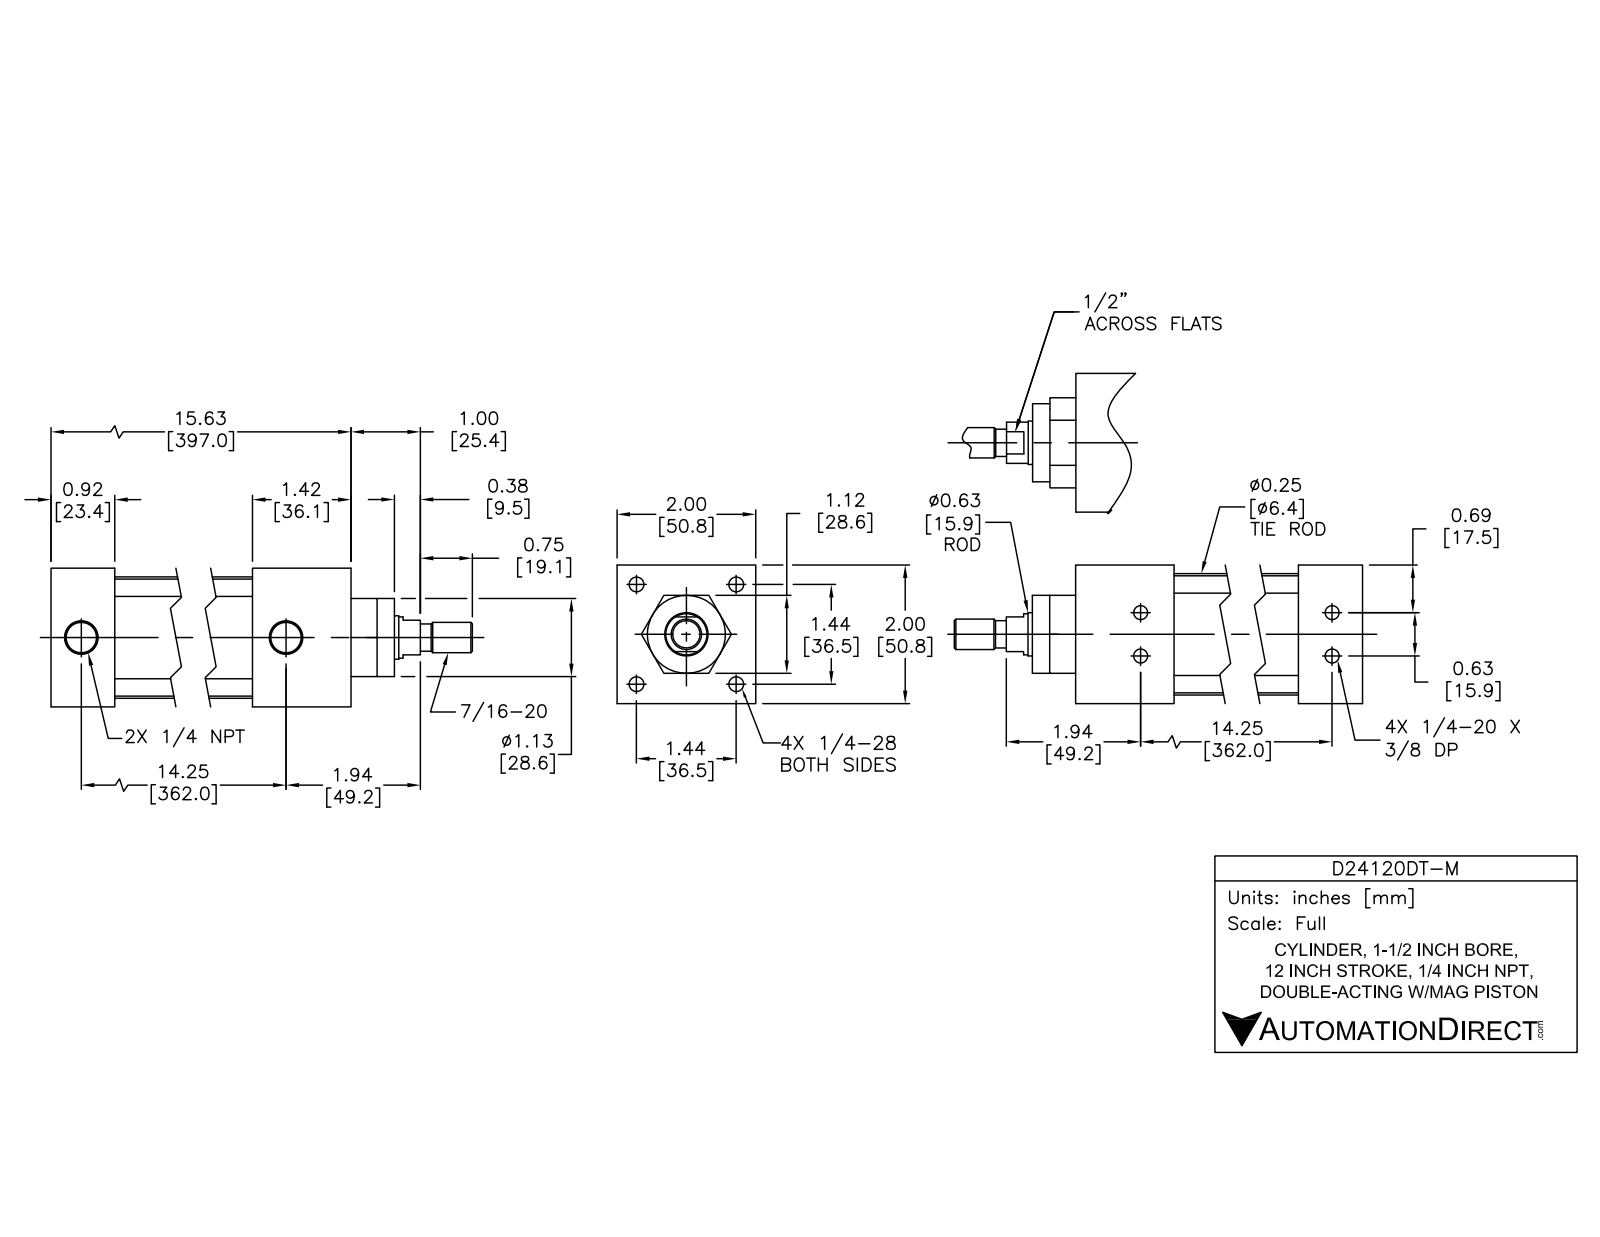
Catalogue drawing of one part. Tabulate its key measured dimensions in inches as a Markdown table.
| quantity | value |
| --- | --- |
| part name | D24120DT-M BODY; D24120DT-M PISTON; D24120DT-M |
| STEP written by | SolidWorks 2015 (AUTOMOTIVE_DESIGN) |
| units | inches |
| bodies | 12 solids, 303 faces (99 planar, 114 cylindrical, 90 other) |
| overall size | 17.371 × 2 × 2 |
| volume | 25.85 in³ |
| surface area | 272.5 in² |
| round holes (diameter × count) | 0.196 × 4, 0.211 × 4, 0.281 × 4, 0.406 × 4, 0.297 × 2, 0.477 × 2, 0.625 × 1, 0.628 × 1, 1.5 × 1 |
| round bosses / shafts (diameter × count) | 0.39 × 4, 0.25 × 4, 0.222 × 4, 1.75 × 1, 1.497 × 1, 1.121 × 1, 0.622 × 1, 0.59 × 1 |
| partial cylindrical surfaces (radius × count) | 0.2 × 4 |
| main face-to-face distances | 2, 0.08, 13.201, 15.621, 1.42, 14.201, 14.701, 13.281, 0.92, 1.121 |
| hole center spacings | 14.25, 0.312, 0.313, 0.625, 1.014, 1.014, 1.434, 1.434 |
